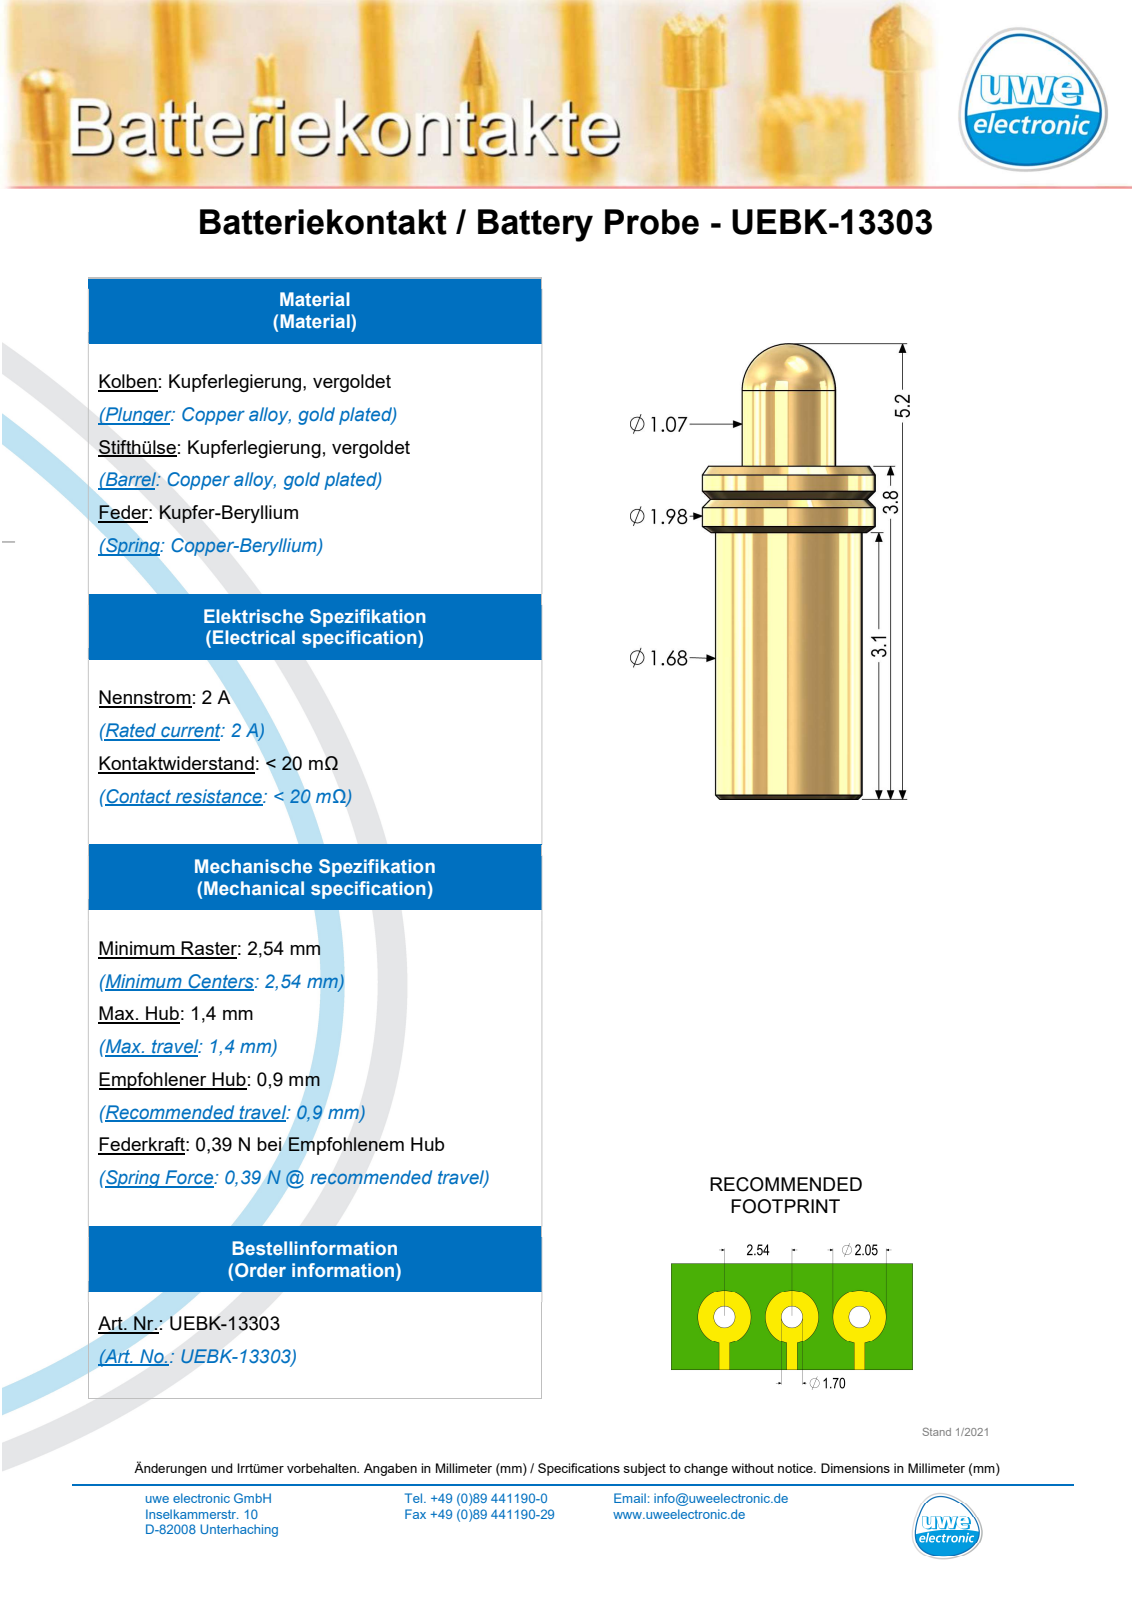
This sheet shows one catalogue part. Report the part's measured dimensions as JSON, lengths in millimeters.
{"part_name": "UEBK-13303", "step_written_by": "SolidWorks 2019 (AUTOMOTIVE_DESIGN)", "units": "millimeters", "bodies": {"solids": 1, "faces": 23, "planar": 3, "cylindrical": 8, "other": 12}, "overall_size": [5.21, 1.98, 1.98], "volume_mm3": 10, "surface_area_mm2": 30, "round_bosses_or_shafts": [[1.98, 1], [1.68, 1], [1.07, 1]], "face_to_face_distances": [3.81, 3.05, 0.76]}
